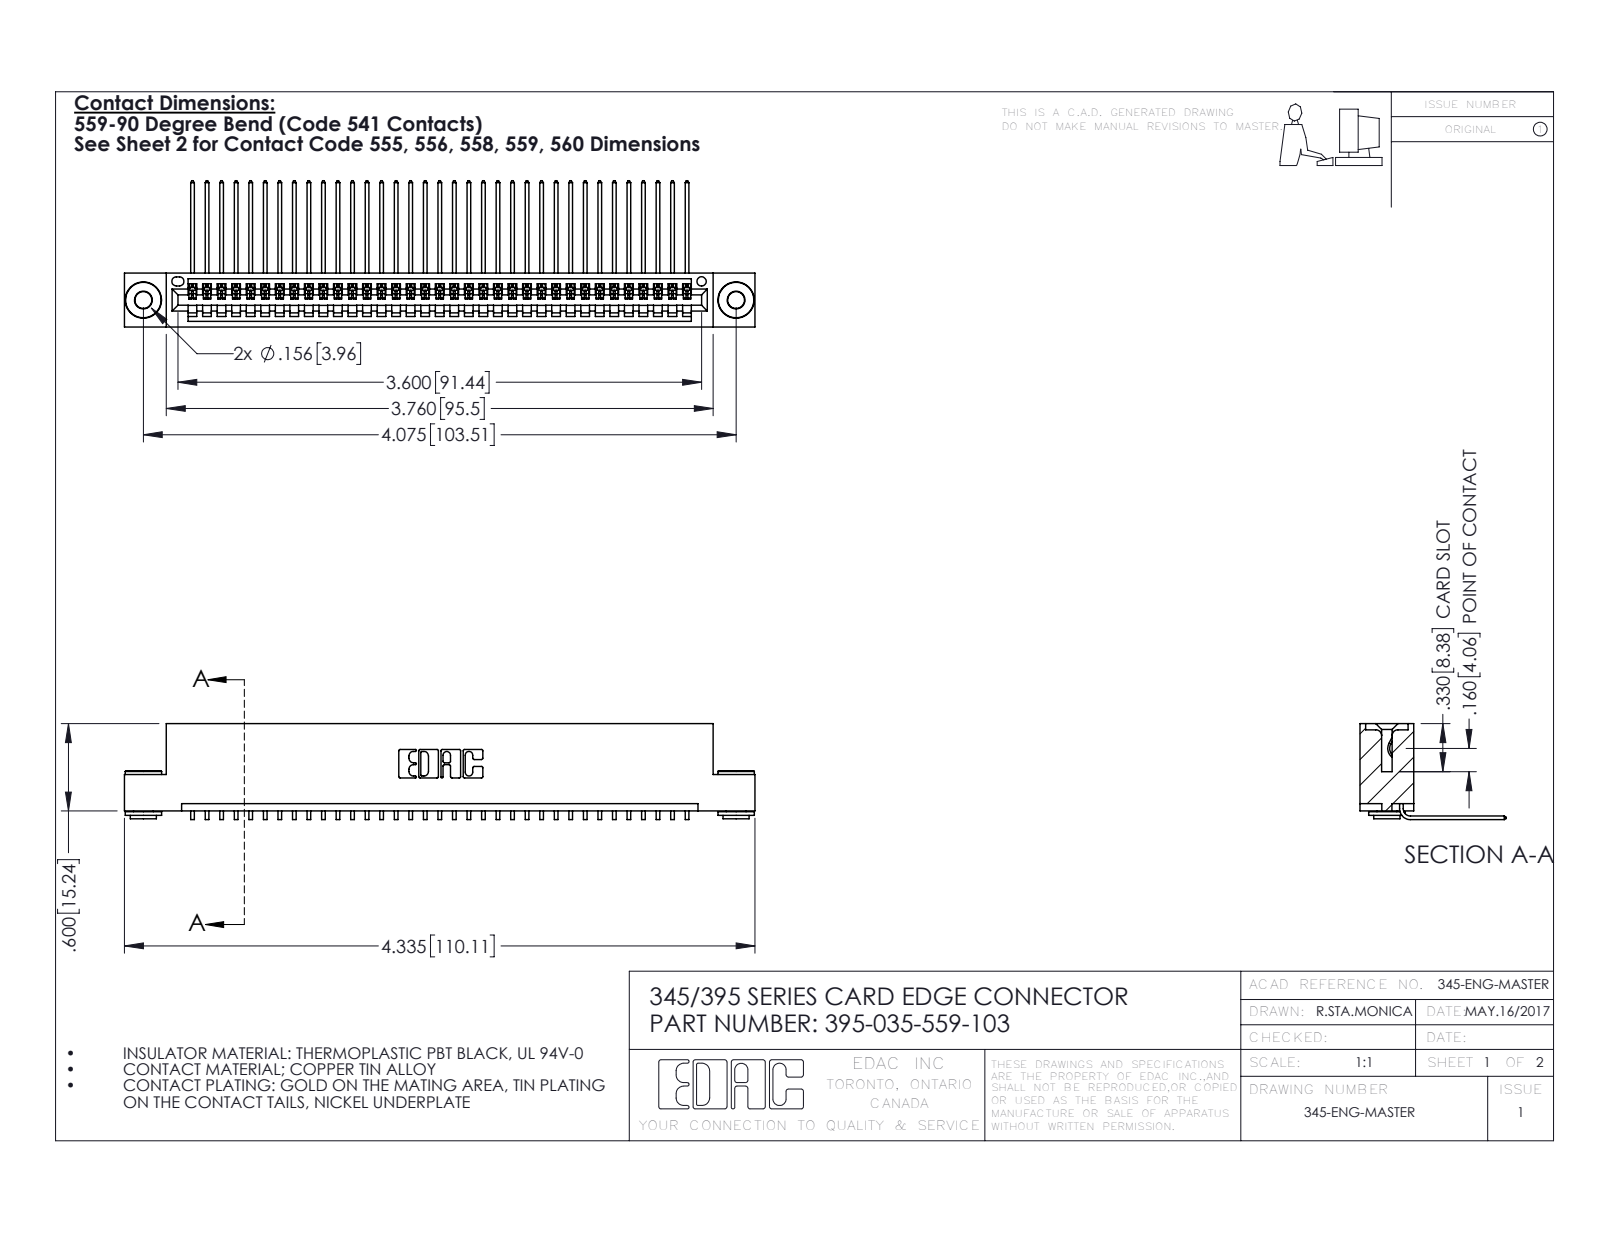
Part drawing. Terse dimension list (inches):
name: 345-292-001_558 559 Tail - 1; 345-250-002_345-250-002-102; 345 Part_Flush Mounting Lugs - 0.156 Dia-TH; 395-035-559-103
written by: SolidWorks 2016 (CONFIG_CONTROL_DESIGN)
unit: in
bodies: 38 solids, 2264 faces (1560 planar, 696 cylindrical, 8 other)
size: 4.335 × 1.005 × 0.659
volume: 0.643 in³; area: 22.95 in²
holes: 2× ⌀0.116, 2× ⌀0.156, 1× ⌀0.064
bosses: 2× ⌀0.25, 2× ⌀0.18, 2× ⌀0.136
rounds: 70× R0.006, 22× R0.01, 6× R0.007, 6× R0.031, 3× R0.026, 2× R0.031, 2× R0.04, 1× R0.014
face distances: 0.072, 0.298, 0.37, 0.2, 0.025, 0.098, 0.272, 0.225, 0.149, 0.072
hole spacings: 0.27, 3.839, 4.075
